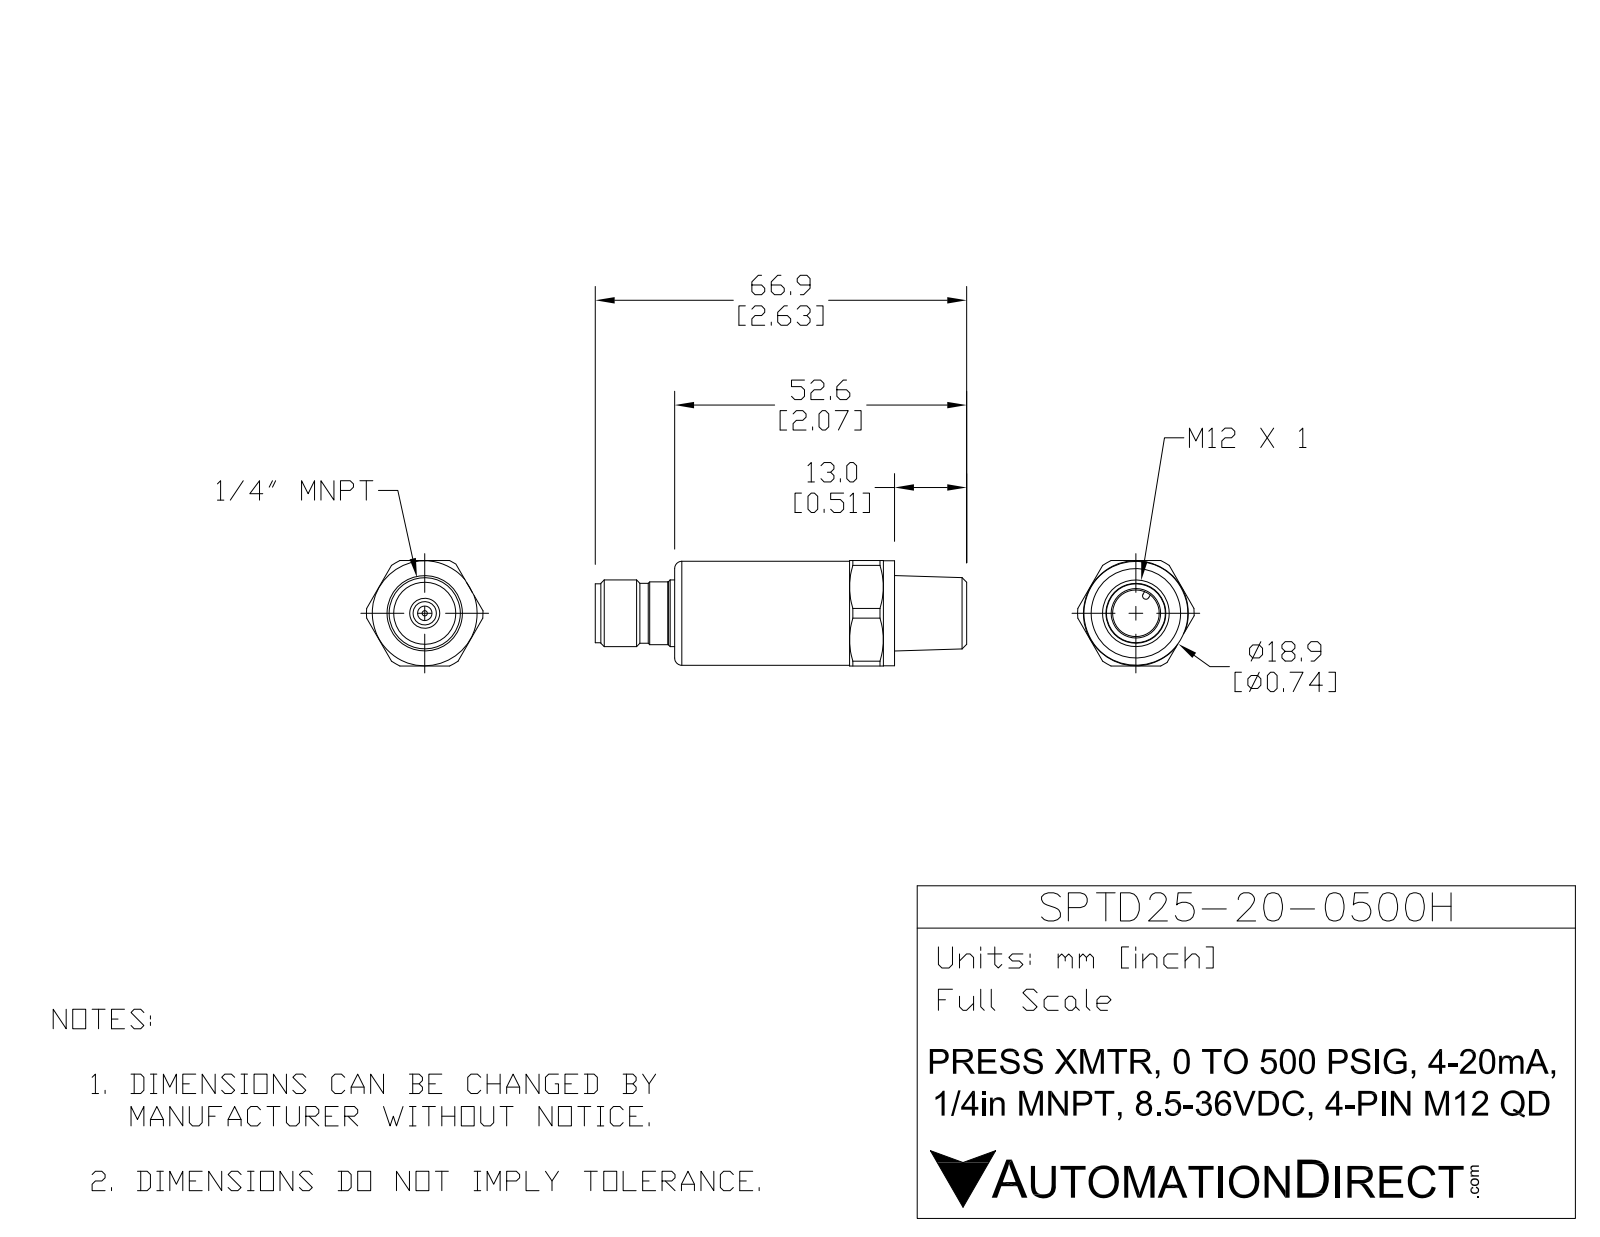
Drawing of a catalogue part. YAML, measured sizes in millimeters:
part_name: "SPDT25-20-0500H"
step_written_by: "SolidWorks 2015 (AUTOMOTIVE_DESIGN)"
units: millimeters
bodies: {solids: 7, faces: 177, planar: 44, cylindrical: 53, other: 80}
overall_size: [66.9, 21.57, 18.9]
volume: 13446
surface_area: 5337
round_holes:
  - {diameter: 4.2, count: 1}
  - {diameter: 8.4, count: 1}
  - {diameter: 16.6, count: 1}
round_bosses_or_shafts:
  - {diameter: 1.4, count: 4}
  - {diameter: 1, count: 4}
  - {diameter: 18.9, count: 1}
  - {diameter: 12, count: 1}
  - {diameter: 11.3, count: 1}
  - {diameter: 10.8, count: 1}
  - {diameter: 10.6, count: 1}
  - {diameter: 10.5, count: 1}
partial_cylinders:
  - {radius: 0.61, count: 1}
face_to_face_distances: [18.9, 52.55, 13.09, 39.46, 58.1, 45.01, 5.55, 14.29, 1.2, 38.26]
